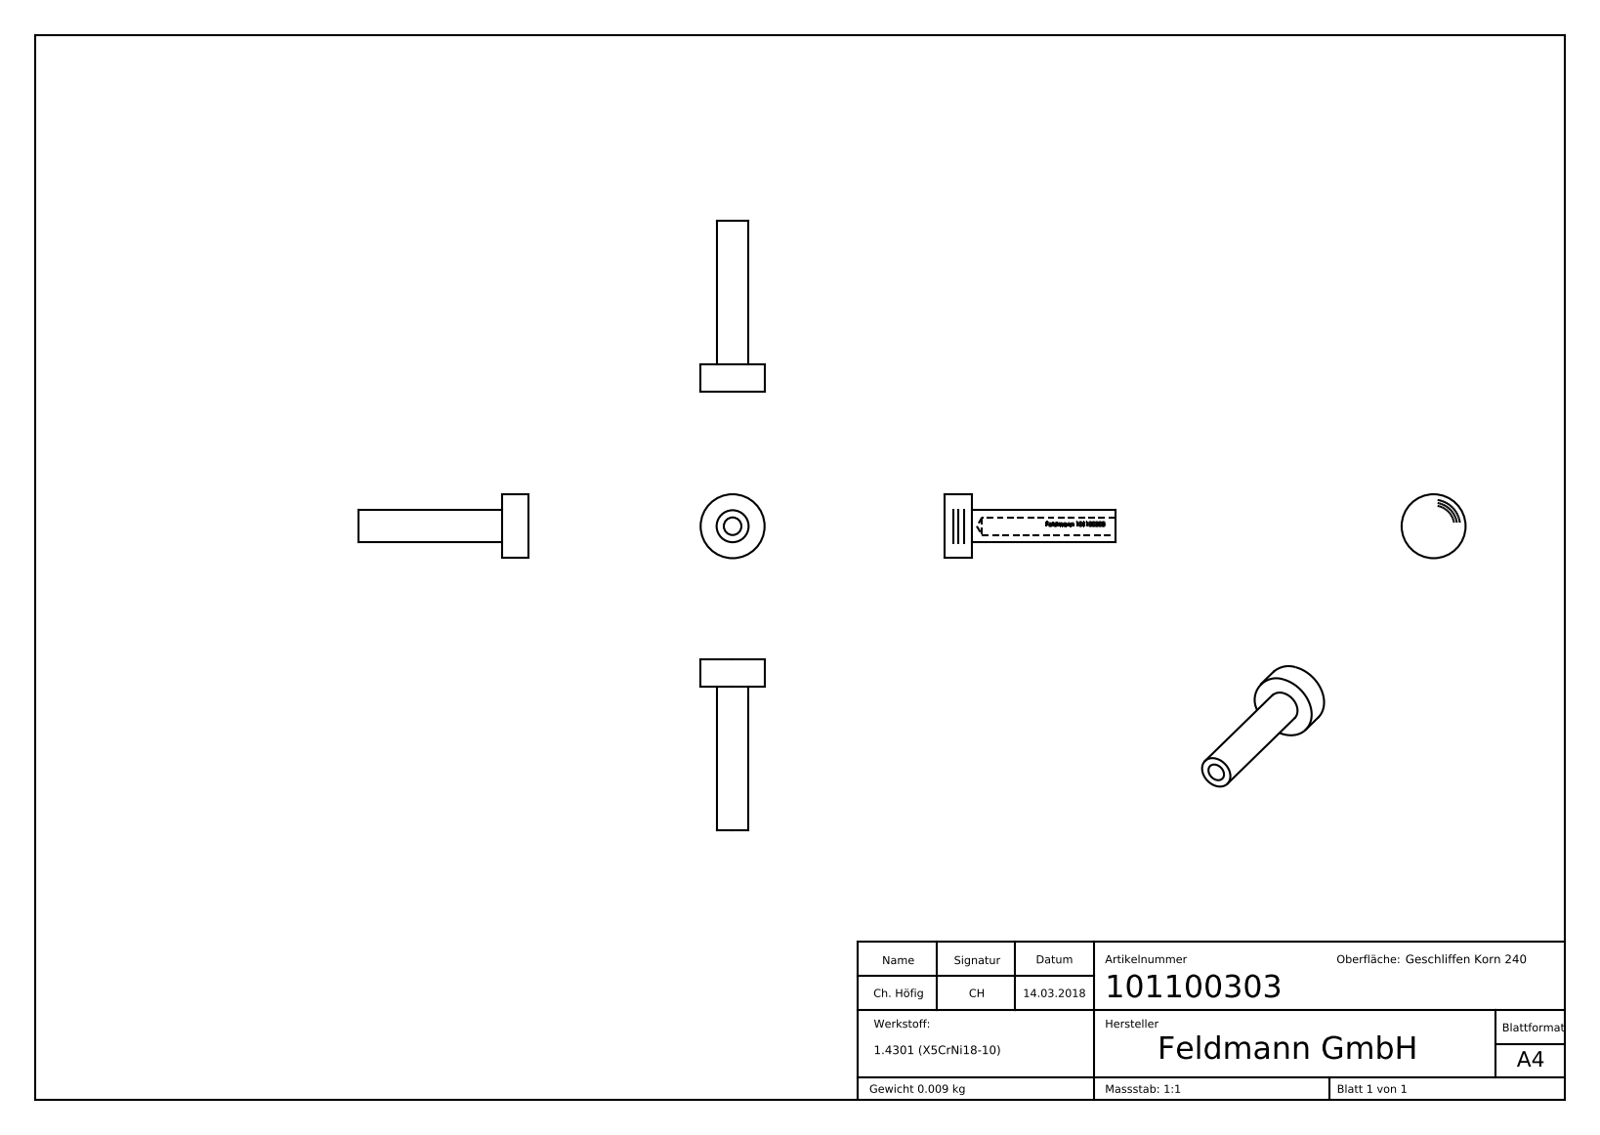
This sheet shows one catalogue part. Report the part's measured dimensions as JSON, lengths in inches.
{"part_name": "101100303", "step_written_by": "SolidWorks 2015 (CONFIG_CONTROL_DESIGN)", "units": "inches", "bodies": {"solids": 1, "faces": 240, "planar": 81, "cylindrical": 45, "other": 114}, "overall_size": [1.26, 0.472, 0.472], "volume_in3": 0.068, "surface_area_in2": 1.845, "round_holes": [[0.13, 1]], "round_bosses_or_shafts": [[0.472, 1], [0.236, 1]], "partial_cylinders_radius": [[0.069, 1]], "face_to_face_distances": [0.197, 1.26, 1.063, 0.024, 0.83, 0.23, 0.254, 0.181, 0.048, 0.072]}
